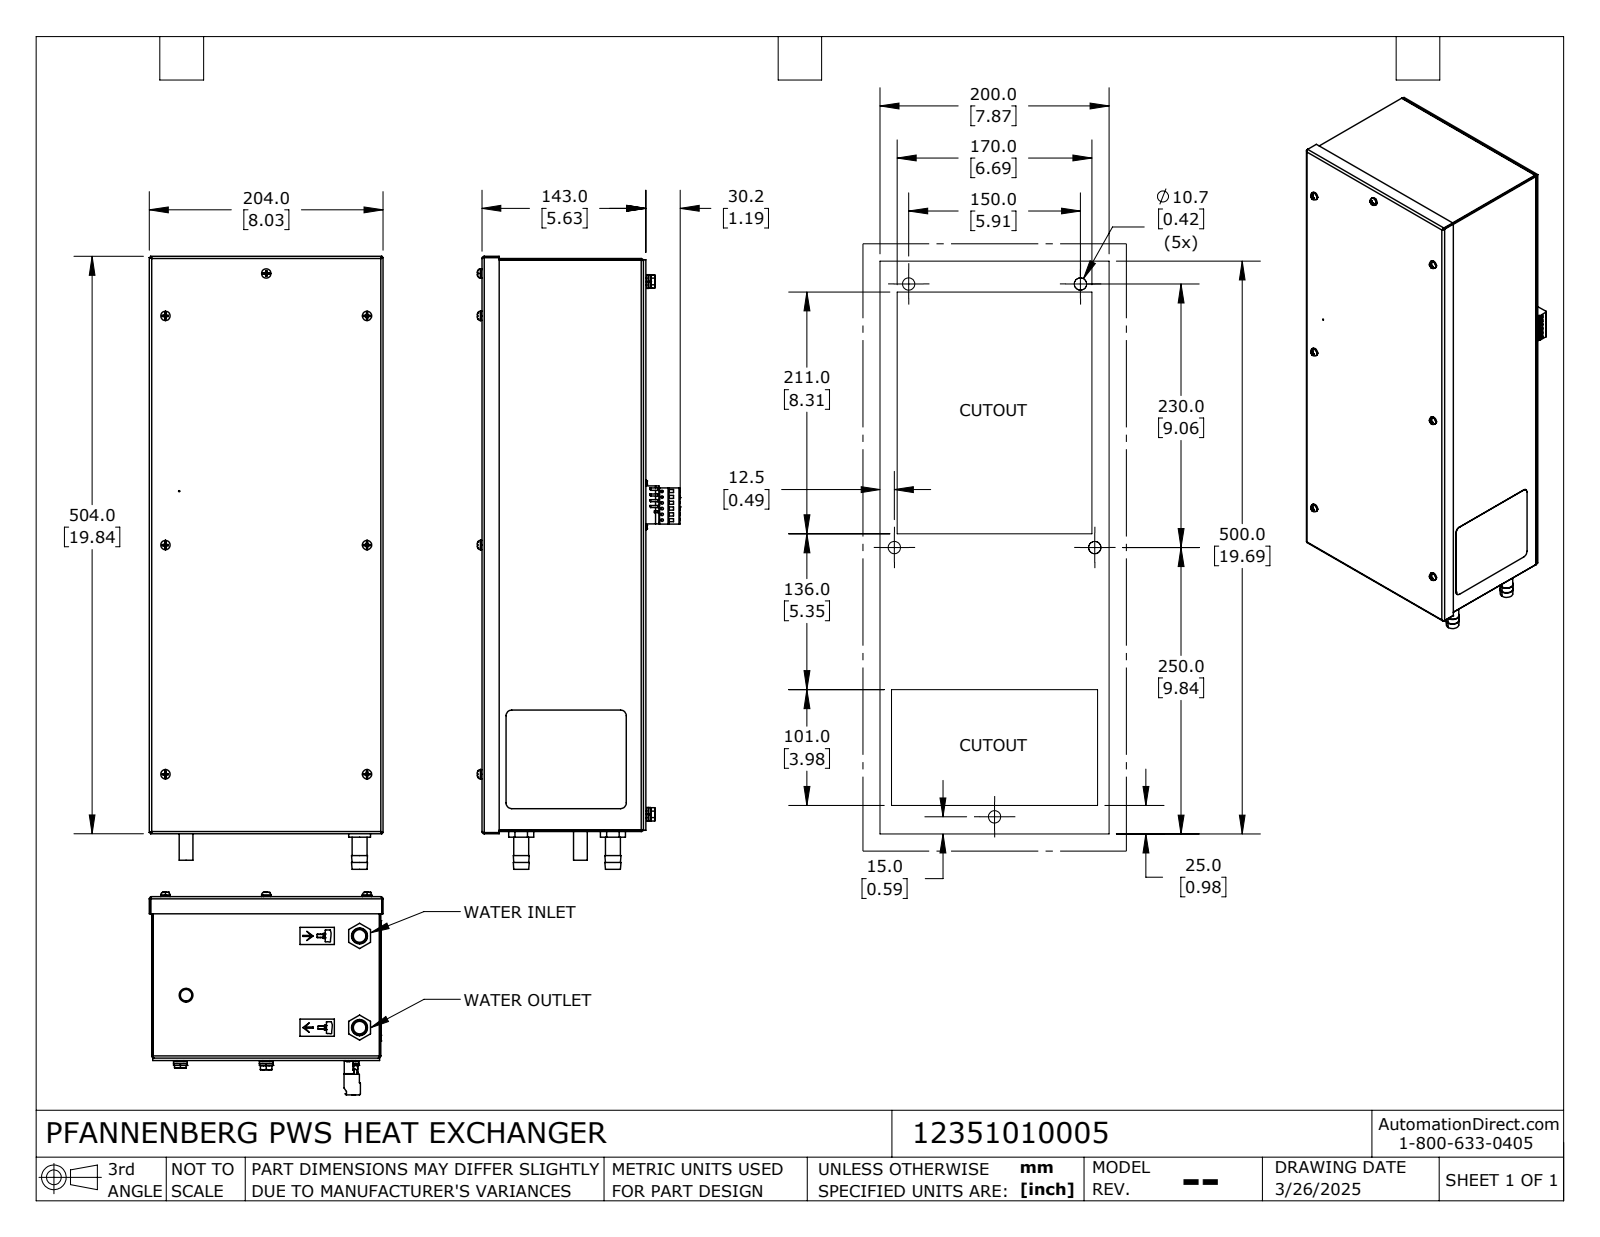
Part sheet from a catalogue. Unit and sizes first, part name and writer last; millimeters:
Units: millimetres
Overall size (bounding box): 535 × 204 × 177.2
Round holes (diameter × count): ⌀4.2 ×20, ⌀4.3 ×7, ⌀4.8 ×7, ⌀7 ×7, ⌀3.6 ×6, ⌀2.3 ×4, ⌀6 ×3, ⌀6.1 ×3, ⌀6.4 ×3, ⌀6.9 ×3, ⌀2.2 ×2, ⌀3.2 ×2
Round bosses / shafts (diameter × count): ⌀8.2 ×7, ⌀8 ×7, ⌀4.2 ×7, ⌀13 ×5, ⌀4 ×4, ⌀12 ×3, ⌀11.8 ×3, ⌀10 ×3
Partial cylindrical surfaces — rounded edges, fillets, slot ends (radius × count): R1 ×22, R2 ×13, R5 ×8, R1.8 ×7, R3 ×6, R3.39 ×6, R1.25 ×3, R1.75 ×3
Main face-to-face distances: 1, 140, 139, 199, 2, 141, 200, 198, 135, 4
Hole centre spacings: 200, 5, 10, 266.08, 15, 400, 0.5, 175.5
Volume: 550 565 mm³ · Surface area: 1 020 000 mm²
Bodies: 51 solids, 2016 faces (1277 planar, 394 cylindrical, 345 other)
Part name (STEP PRODUCT): 12351010005_Default
STEP written by: SolidWorks 2024 (CONFIG_CONTROL_DESIGN)
